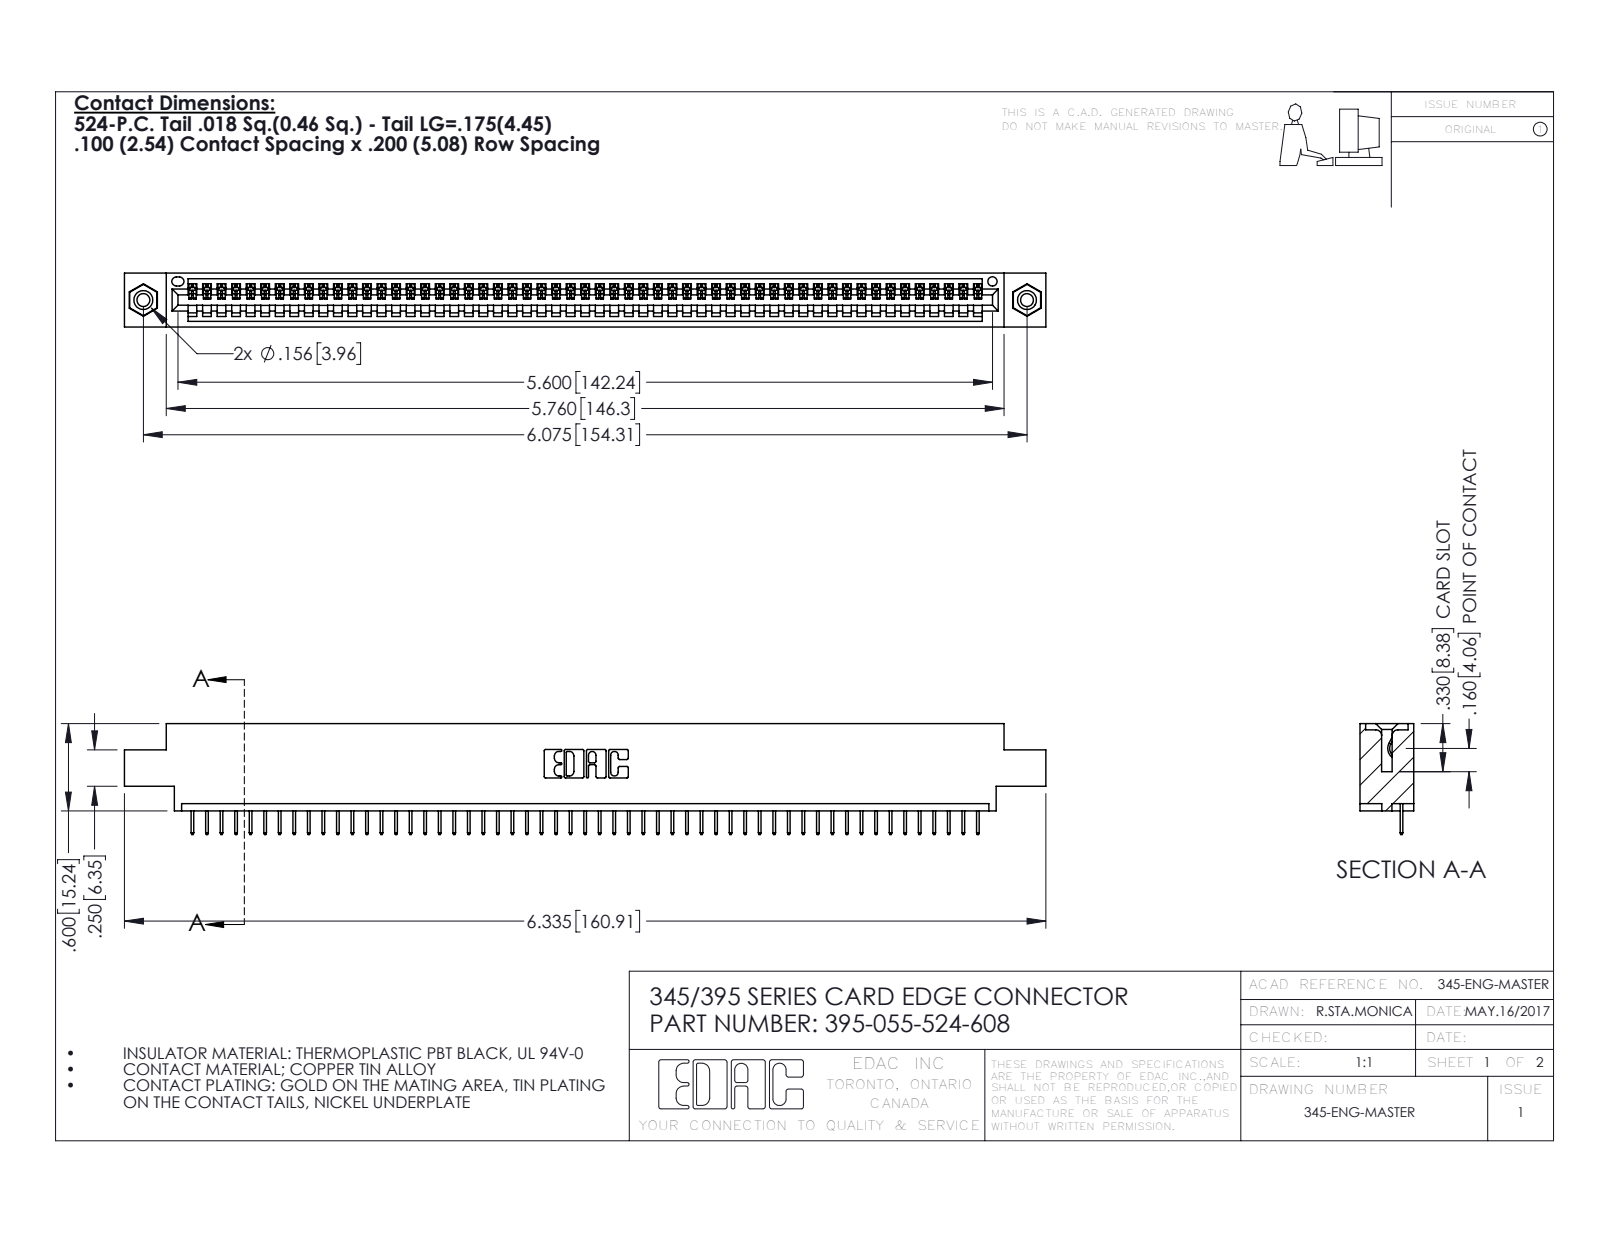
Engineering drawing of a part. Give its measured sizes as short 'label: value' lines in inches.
name: 395-055-524-608; 345-250-001_345-250-003-102; 345 Part_0.170 Offset - 0.156 Dia-TI; 345-292-001_345-293-124
written by: SolidWorks 2016 (CONFIG_CONTROL_DESIGN)
unit: in
bodies: 58 solids, 3600 faces (2646 planar, 938 cylindrical, 16 other)
size: 6.335 × 0.762 × 0.37
volume: 0.919 in³; area: 30.43 in²
holes: 2× ⌀0.089, 2× ⌀0.125, 2× ⌀0.156, 1× ⌀0.064
bosses: 2× ⌀0.155
rounds: 110× R0.006, 22× R0.01, 6× R0.007, 6× R0.031, 3× R0.026, 2× R0.031, 2× R0.04, 1× R0.014
face distances: 0.072, 0.298, 0.37, 0.2, 0.098, 0.272, 0.025, 0.225, 0.072, 0.175
hole spacings: 0.27, 5.839, 6.075
